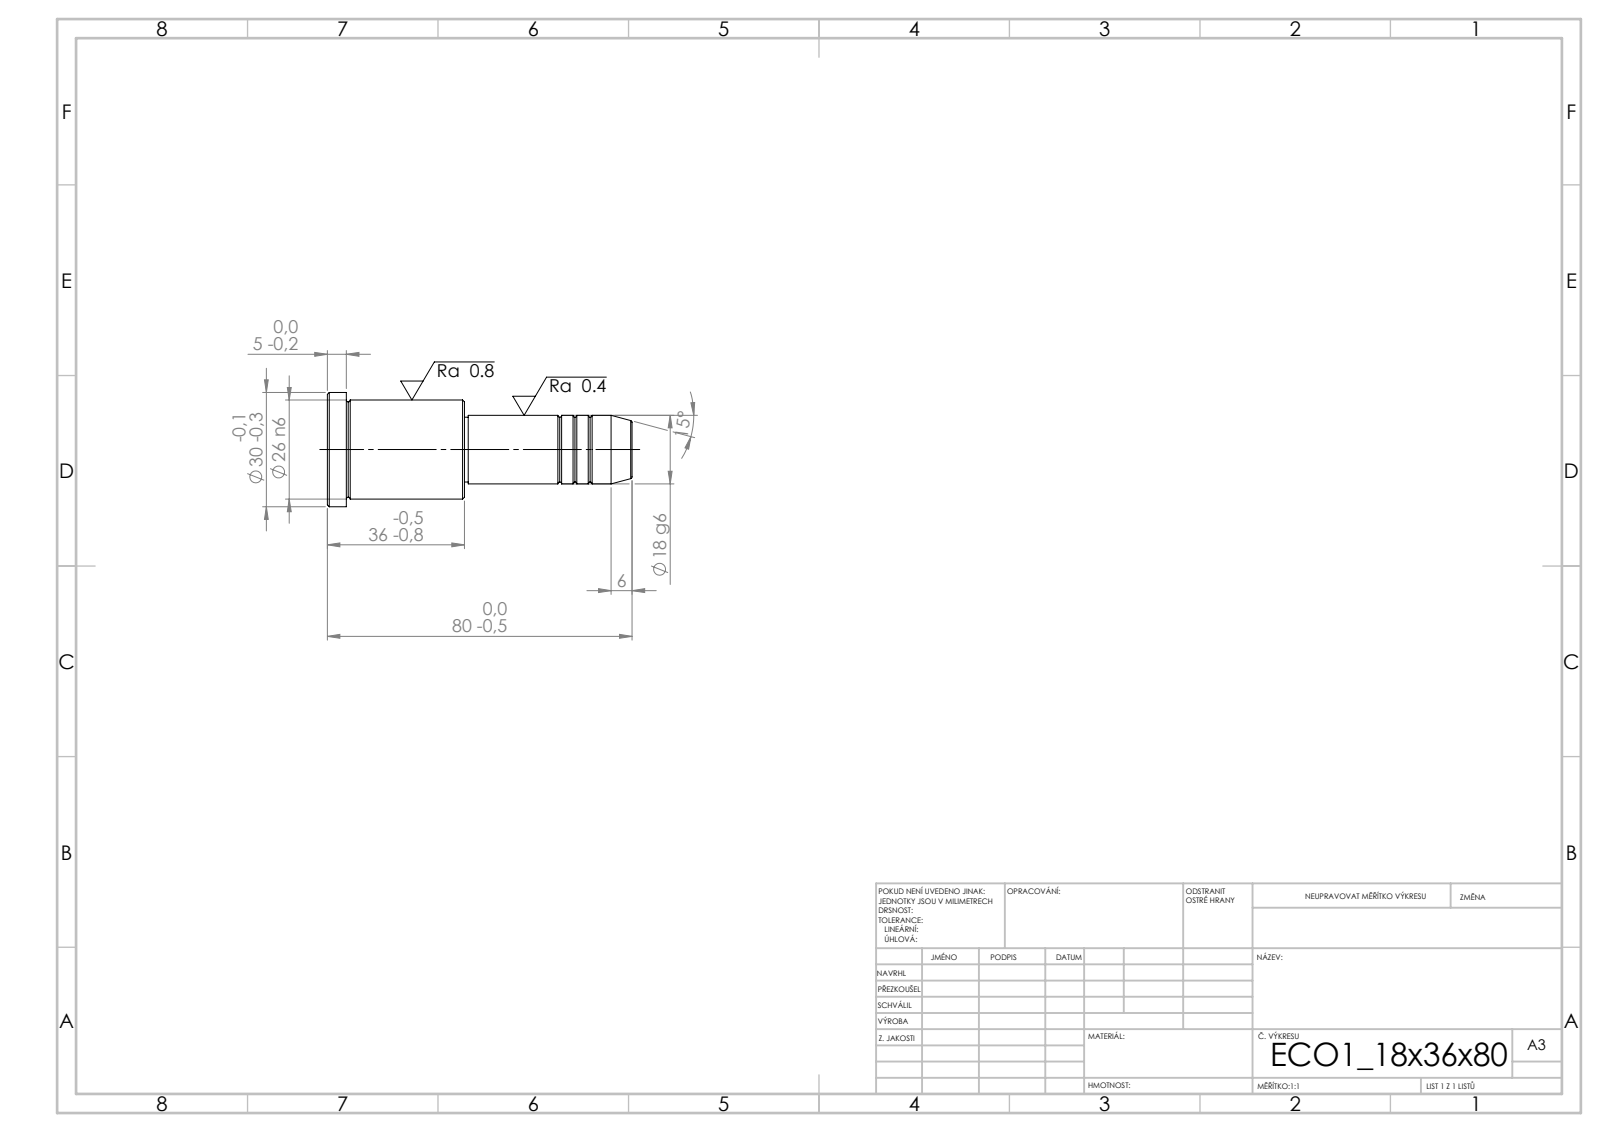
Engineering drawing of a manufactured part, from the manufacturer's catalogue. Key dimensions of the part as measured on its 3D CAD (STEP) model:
STEP written by: SolidWorks 2019 (CONFIG_CONTROL_DESIGN)
Units: millimetres
Bodies: 1 solid, 43 faces (5 planar, 14 cylindrical, 24 other)
Overall size (bounding box): 80 × 30 × 30
Volume: 30 826 mm³ · Surface area: 6 938 mm²
Round bosses / shafts (diameter × count): ⌀30 ×1, ⌀26 ×1, ⌀18 ×1, ⌀17 ×1
Main face-to-face distances: 36, 31, 5, 44, 75, 80, 43, 1, 32, 37
